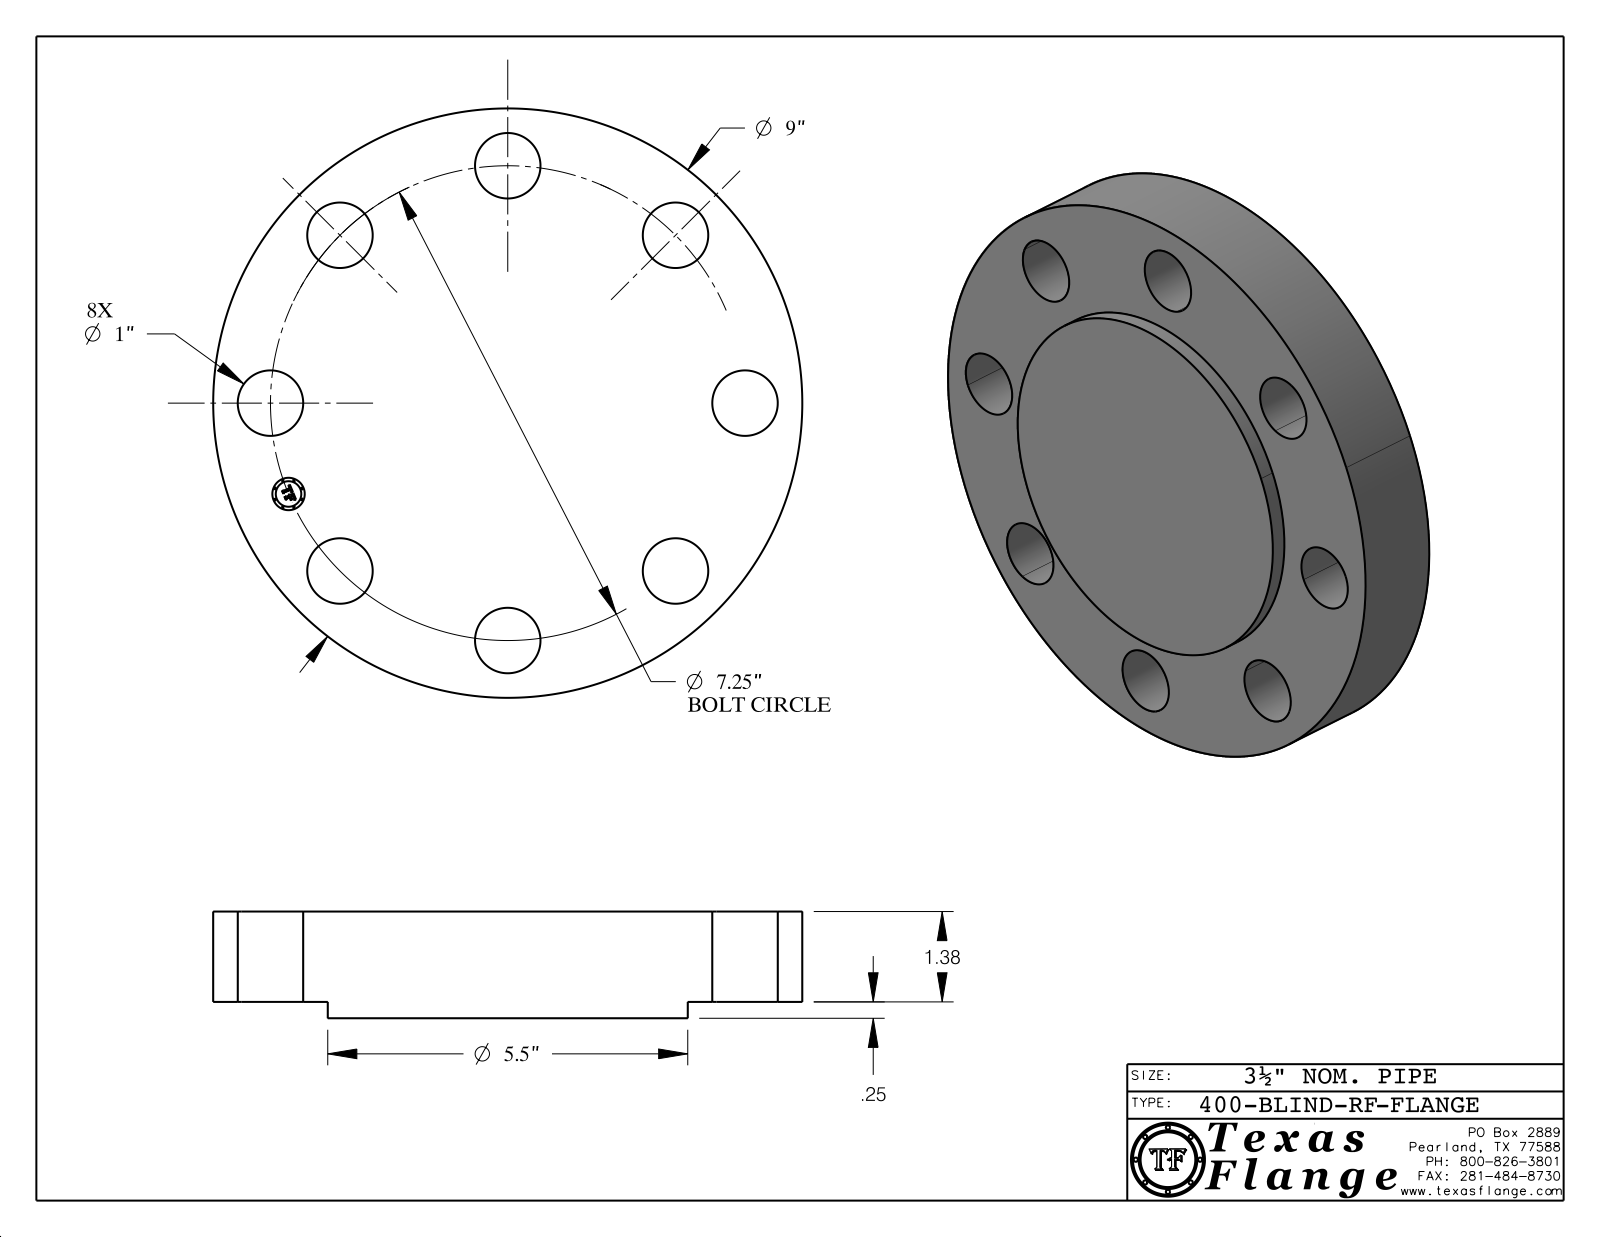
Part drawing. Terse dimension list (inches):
name: 400-BLIND-RF
written by: CATIA V5 STEP AP214 (AUTOMOTIVE_DESIGN)
unit: in
bodies: 1 solid, 408 faces (368 planar, 40 cylindrical, 0 other)
size: 9 × 9 × 1.63
volume: 85.06 in³; area: 192.8 in²
holes: 8× ⌀1, 1× ⌀0.495
bosses: 8× ⌀0.03, 1× ⌀9, 1× ⌀5.5, 1× ⌀0.39
face distances: 1.38, 0.25, 1.63, 1.615, 1.365, 0.015, 0.148, 0.144, 0.027, 0.096
hole spacings: 2.774, 5.127, 6.698, 7.25, 1.415, 7.111, 4.028, 4.028
